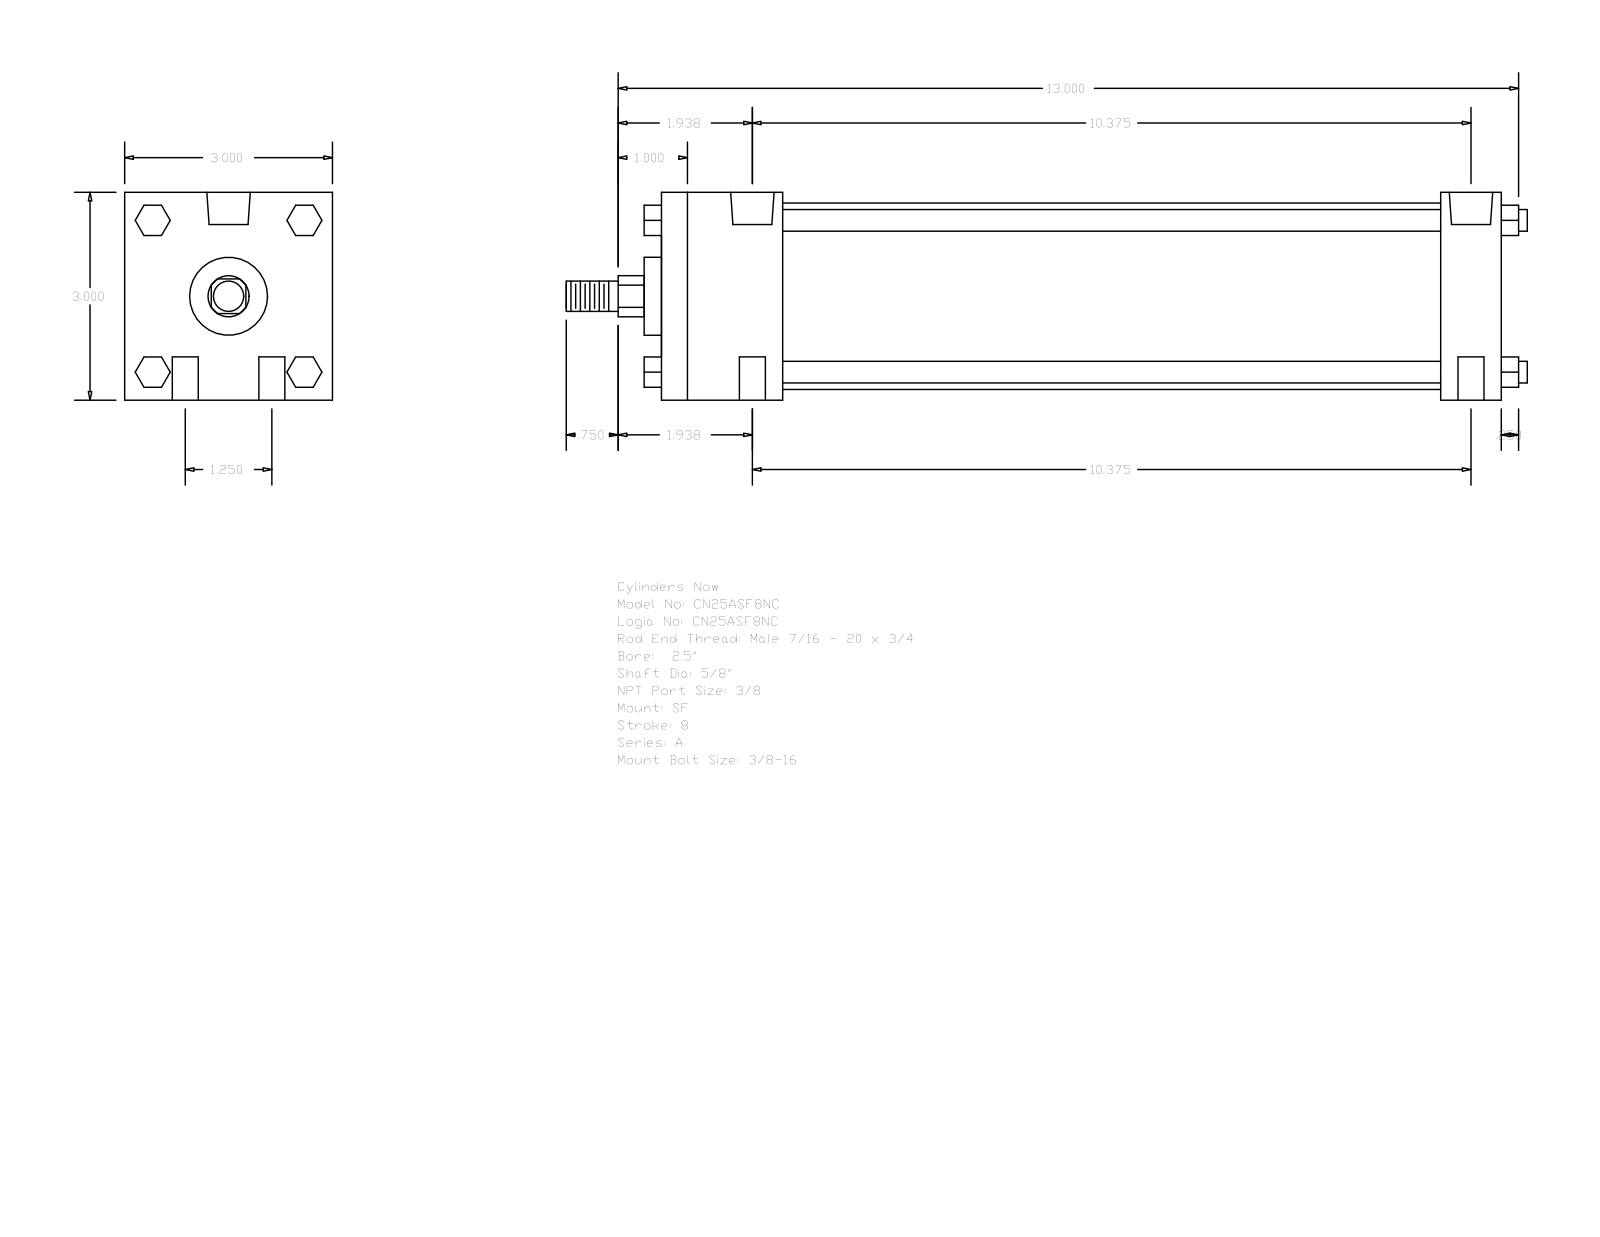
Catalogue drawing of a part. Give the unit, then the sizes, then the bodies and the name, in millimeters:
Units: millimetres
Overall size (bounding box): 352.43 × 76.2 × 76.2
Round holes (diameter × count): ⌀9.53 ×4, ⌀5.56 ×2, ⌀15.93 ×2
Round bosses / shafts (diameter × count): ⌀7.94 ×4, ⌀68.33 ×1, ⌀28.57 ×1, ⌀15.88 ×1, ⌀11.11 ×1
Partial cylindrical surfaces — rounded edges, fillets, slot ends (radius × count): R7.54 ×1
Main face-to-face distances: 76.2, 307.97, 44.45, 285.74, 22.23, 241.29, 263.52, 6.35, 314.32, 50.8
Hole centre spacings: 15.88, 264.01, 263.53, 31.76, 265.44, 268.29
Bodies: 0 solids, 124 faces (94 planar, 30 cylindrical, 0 other)
Part name (STEP PRODUCT): A_SF__0250_0.625
STEP written by: GSSL Pune (CONFIG_CONTROL_DESIGN)
